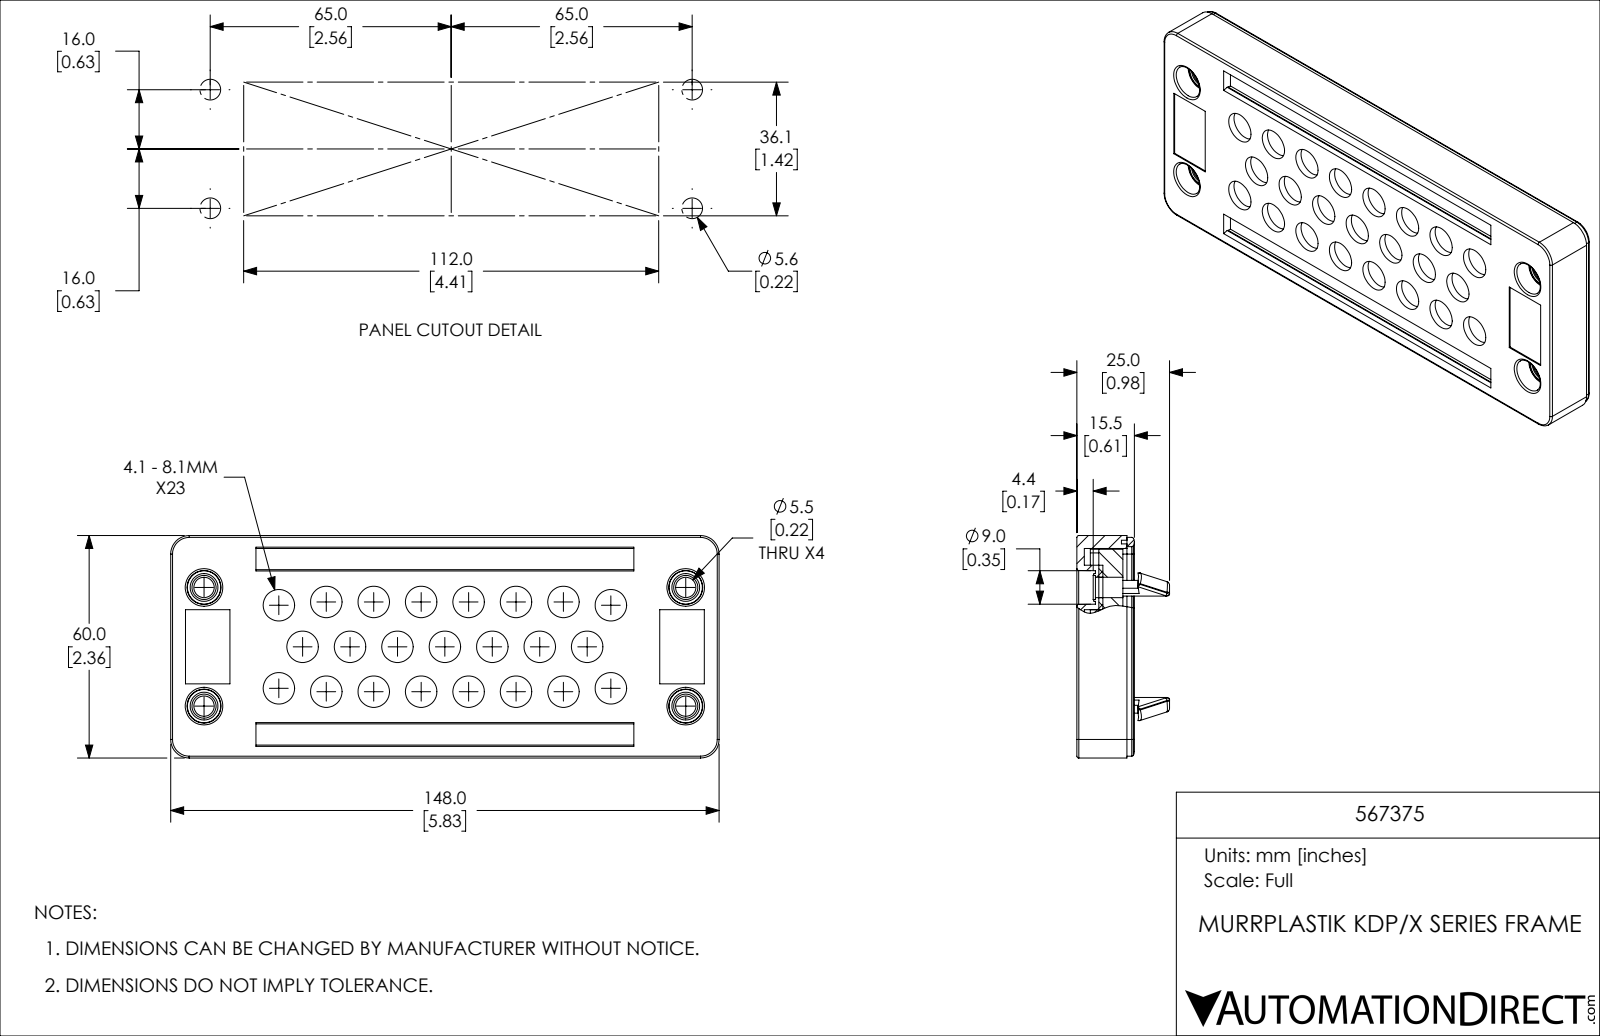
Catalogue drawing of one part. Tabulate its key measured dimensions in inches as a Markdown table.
| quantity | value |
| --- | --- |
| part name | 567375 |
| STEP written by | SolidWorks 2019 (CONFIG_CONTROL_DESIGN) |
| units | inches |
| bodies | 4 solids, 494 faces (170 planar, 272 cylindrical, 52 other) |
| overall size | 5.827 × 2.362 × 0.984 |
| volume | 4.819 in³ |
| surface area | 102.1 in² |
| round holes (diameter × count) | 0.335 × 23, 0.472 × 23, 0.217 × 4, 0.256 × 4 |
| round bosses / shafts (diameter × count) | 0.295 × 4 |
| partial cylindrical surfaces (radius × count) | 0.039 × 28, 0.02 × 12, 0.079 × 12, 0.118 × 8, 0.059 × 4, 0.108 × 4, 0.128 × 4, 0.138 × 4 |
| main face-to-face distances | 0.091, 0.232, 0.142, 0.256, 0.488, 0.346, 0.079, 0.063, 0.154, 0.409 |
| hole center spacings | 0.539, 0.893, 0.504, 1.347, 1.008, 1.827, 1.078, 1.512 |
